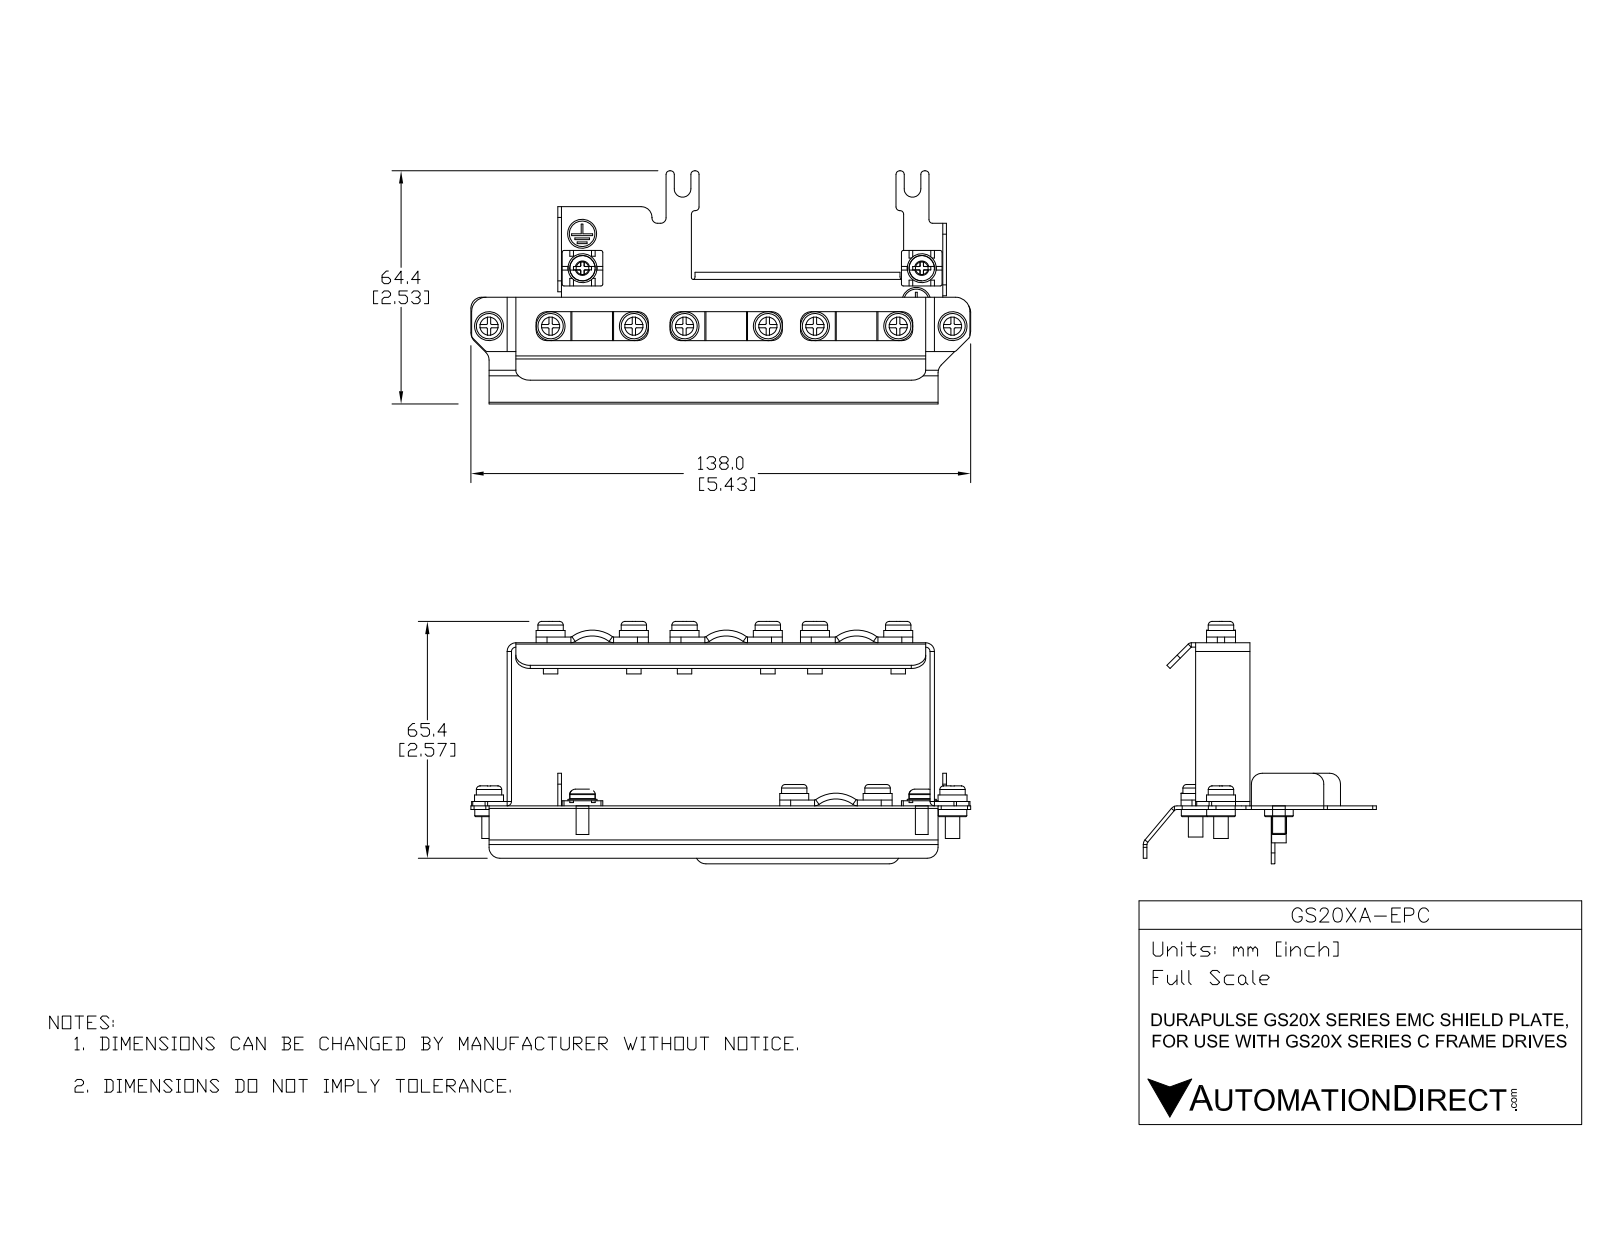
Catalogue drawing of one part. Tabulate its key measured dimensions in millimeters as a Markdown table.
| quantity | value |
| --- | --- |
| part name | GS20XA-EPC |
| STEP written by | SolidWorks 2017 (AUTOMOTIVE_DESIGN) |
| units | millimeters |
| bodies | 20 solids, 1209 faces (838 planar, 289 cylindrical, 82 other) |
| overall size | 138 × 66.9 × 64.4 |
| volume | 18 260 mm³ |
| surface area | 32 820 mm² |
| round holes (diameter × count) | 4 × 10, 4.5 × 8, 5.5 × 2, 3.3 × 1, 8 × 1, 8 × 1 |
| round bosses / shafts (diameter × count) | 7 × 12, 8 × 11, 4 × 2, 7.9 × 1, 7.1 × 1, 7.1 × 1, 6.6 × 1, 5.4 × 1 |
| partial cylindrical surfaces (radius × count) | 0.3 × 44, 3 × 31, 1 × 22, 0.5 × 18, 2.1 × 8, 1.2 × 5, 4 × 4, 8 × 4 |
| main face-to-face distances | 1, 1.2, 45, 46, 43.8, 44.8, 116.8, 35.4, 1.6, 115.6 |
| hole center spacings | 23, 9, 31.1, 36, 37, 67.7, 73, 8.4 |
